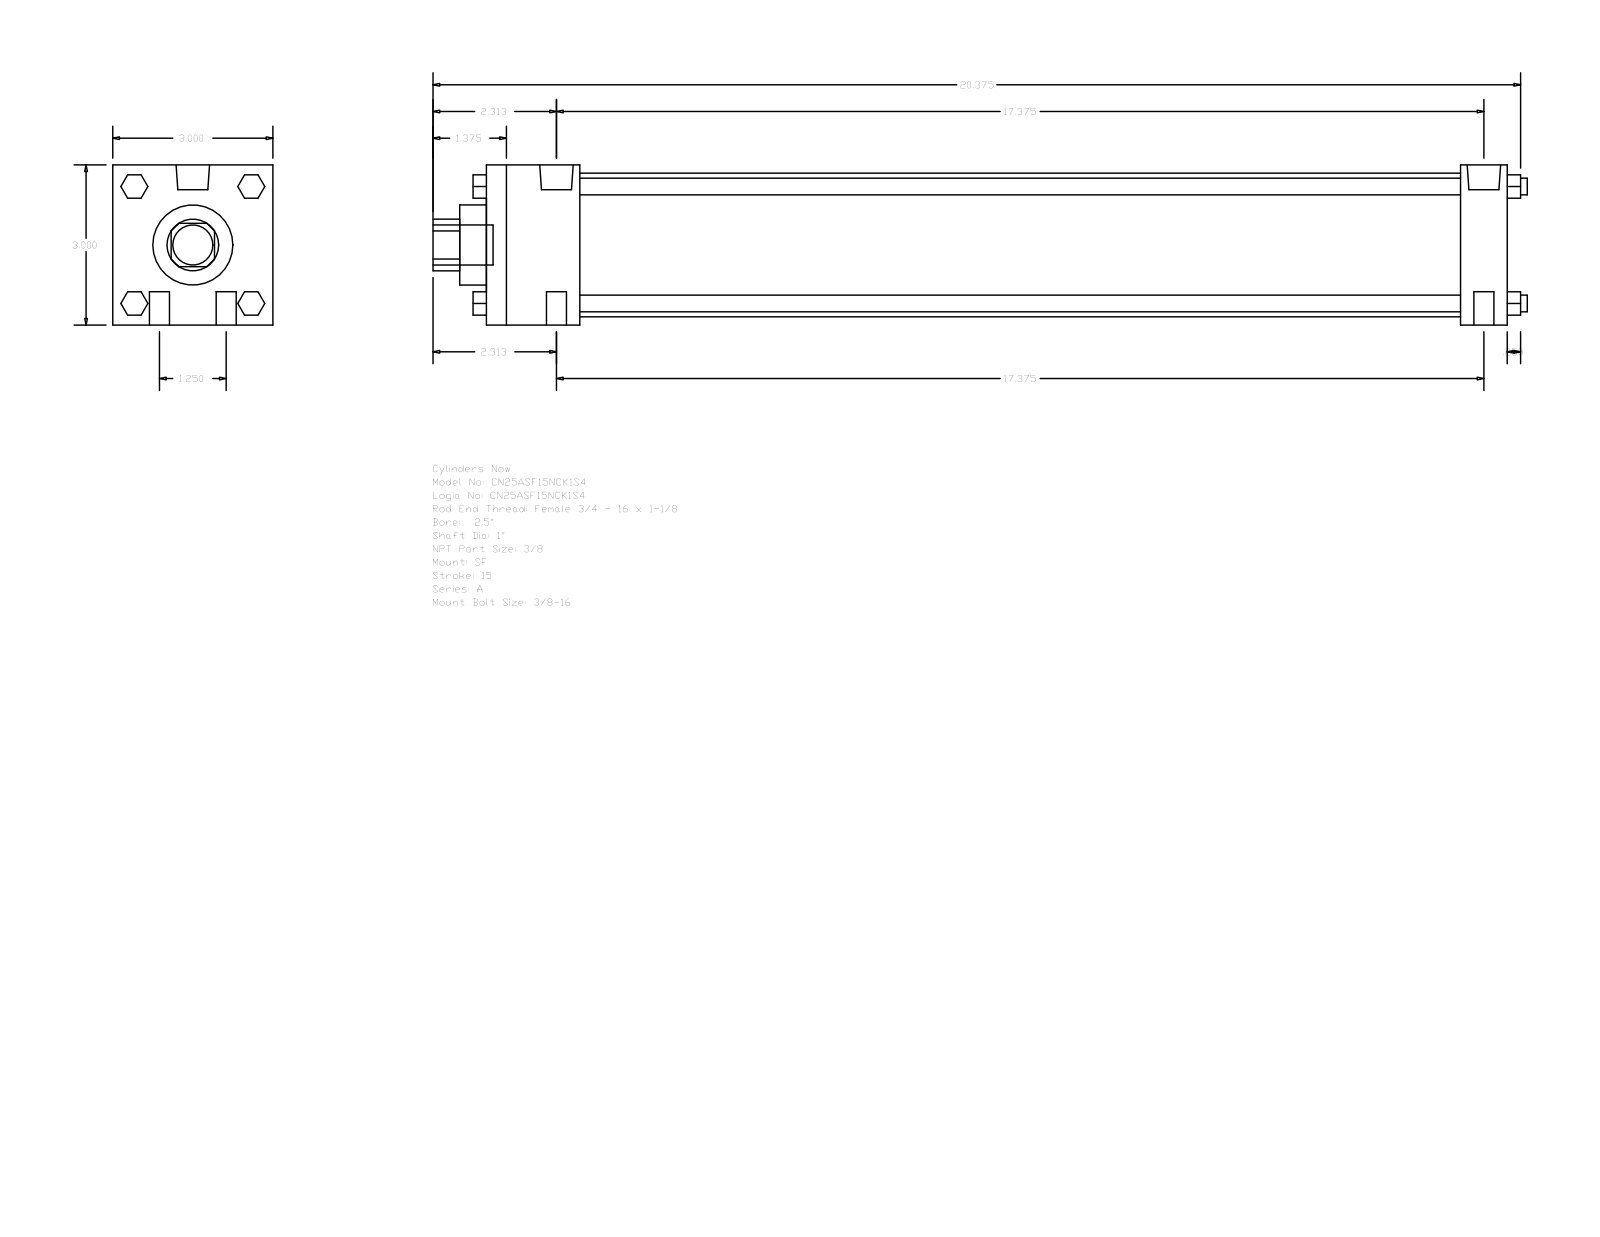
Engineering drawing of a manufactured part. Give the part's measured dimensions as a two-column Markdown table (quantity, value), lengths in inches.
| quantity | value |
| --- | --- |
| part name | A_SF__0250_1 |
| STEP written by | GSSL Pune (CONFIG_CONTROL_DESIGN) |
| units | inches |
| bodies | 0 solids, 124 faces (94 planar, 30 cylindrical, 0 other) |
| overall size | 20.5 × 3 × 3 |
| round holes (diameter × count) | 1 × 1, 1.5 × 1, 2.69 × 1 |
| round bosses / shafts (diameter × count) | 0.375 × 4, 0.313 × 4, 0.627 × 2, 0.219 × 2, 0.75 × 1 |
| partial cylindrical surfaces (radius × count) | 0.484 × 1 |
| main face-to-face distances | 3, 19.125, 18.25, 0.875, 1.75, 16.5, 17.375, 0.5, 0.437, 2.25 |
